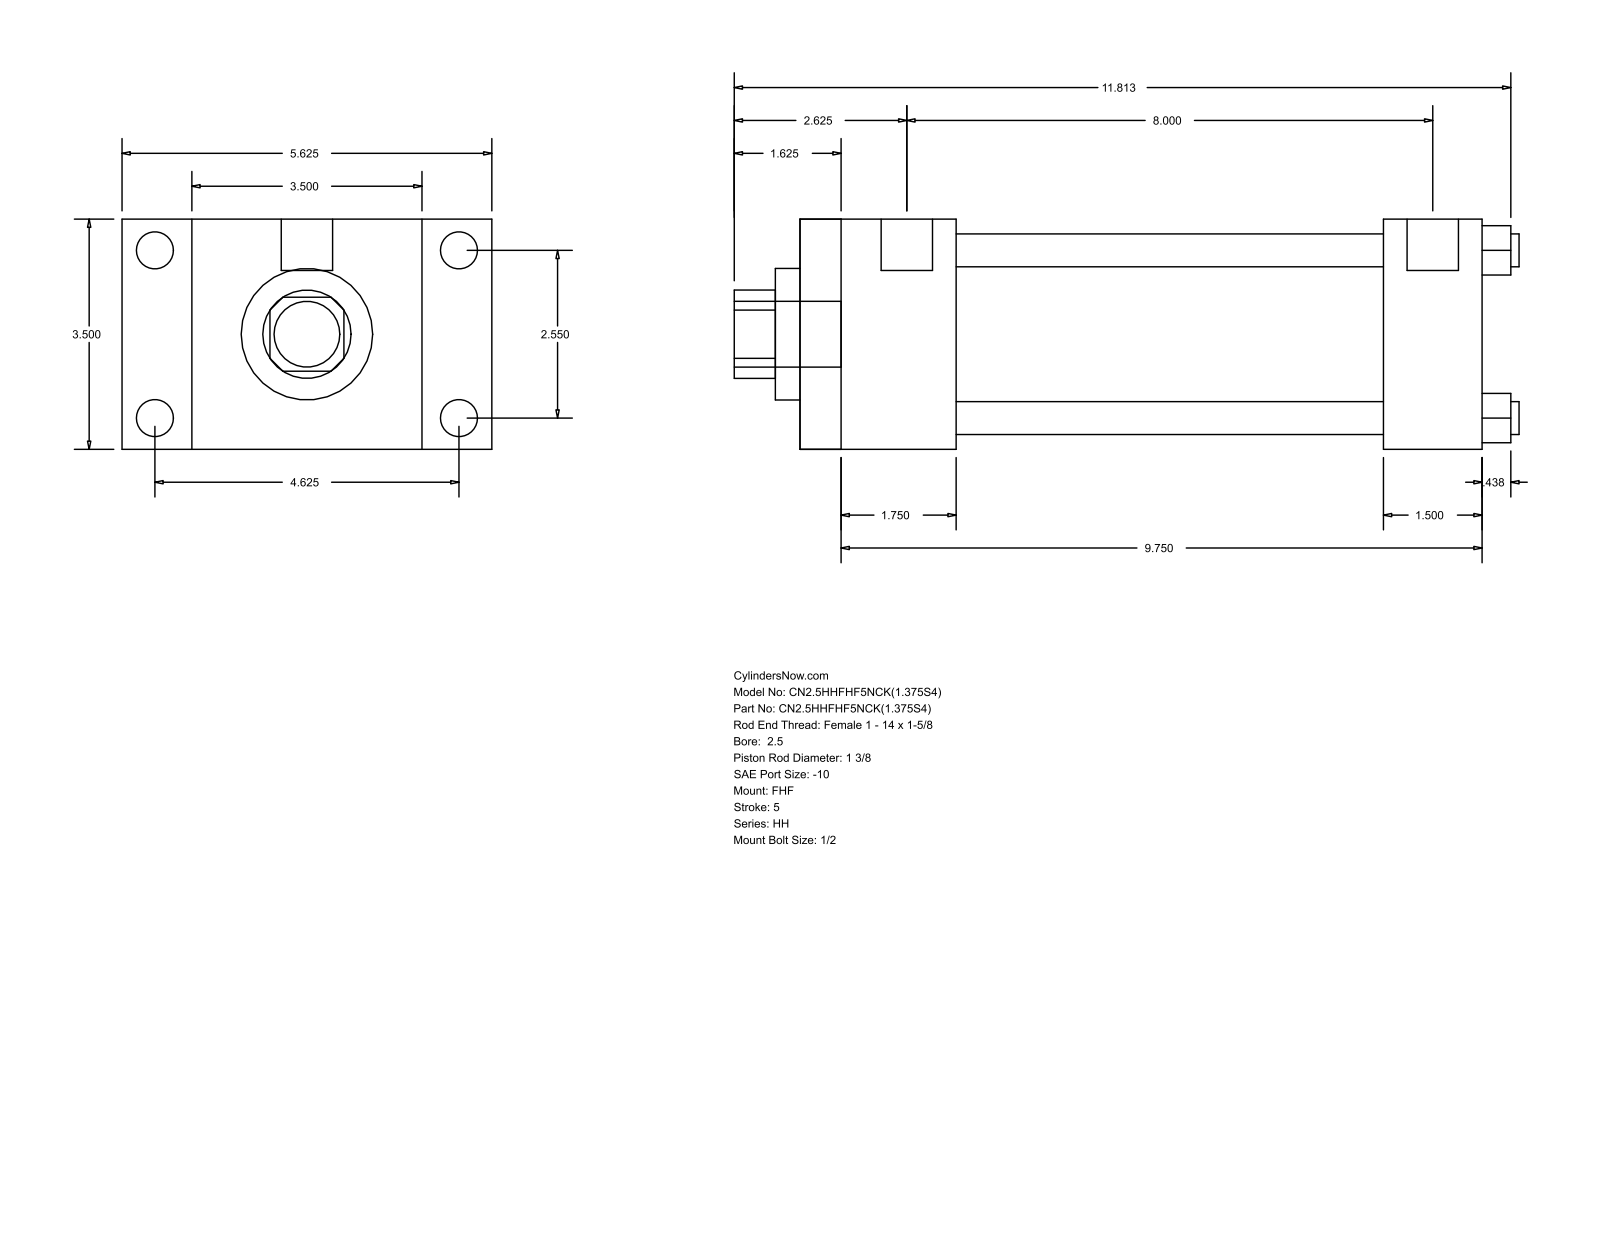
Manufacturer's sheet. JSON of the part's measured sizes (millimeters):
{"part_name": "HH_FHF__0250_1.375", "step_written_by": "GSSL Pune (CONFIG_CONTROL_DESIGN)", "units": "millimeters", "bodies": {"solids": 0, "faces": 88, "planar": 60, "cylindrical": 28, "other": 0}, "overall_size": [303.21, 142.88, 88.9], "round_holes": [[12.7, 4], [34.92, 1], [50.8, 1], [73.03, 1]], "round_bosses_or_shafts": [[14.3, 4], [5.56, 4], [19.84, 2], [25.4, 1]], "partial_cylinders_radius": [[17.06, 1]], "face_to_face_distances": [88.9, 60.32, 26.99, 115.89, 263.53, 203.21, 142.88, 225.42, 165.1, 38.11], "hole_center_spacings": [45.79, 64.76, 91.58]}
